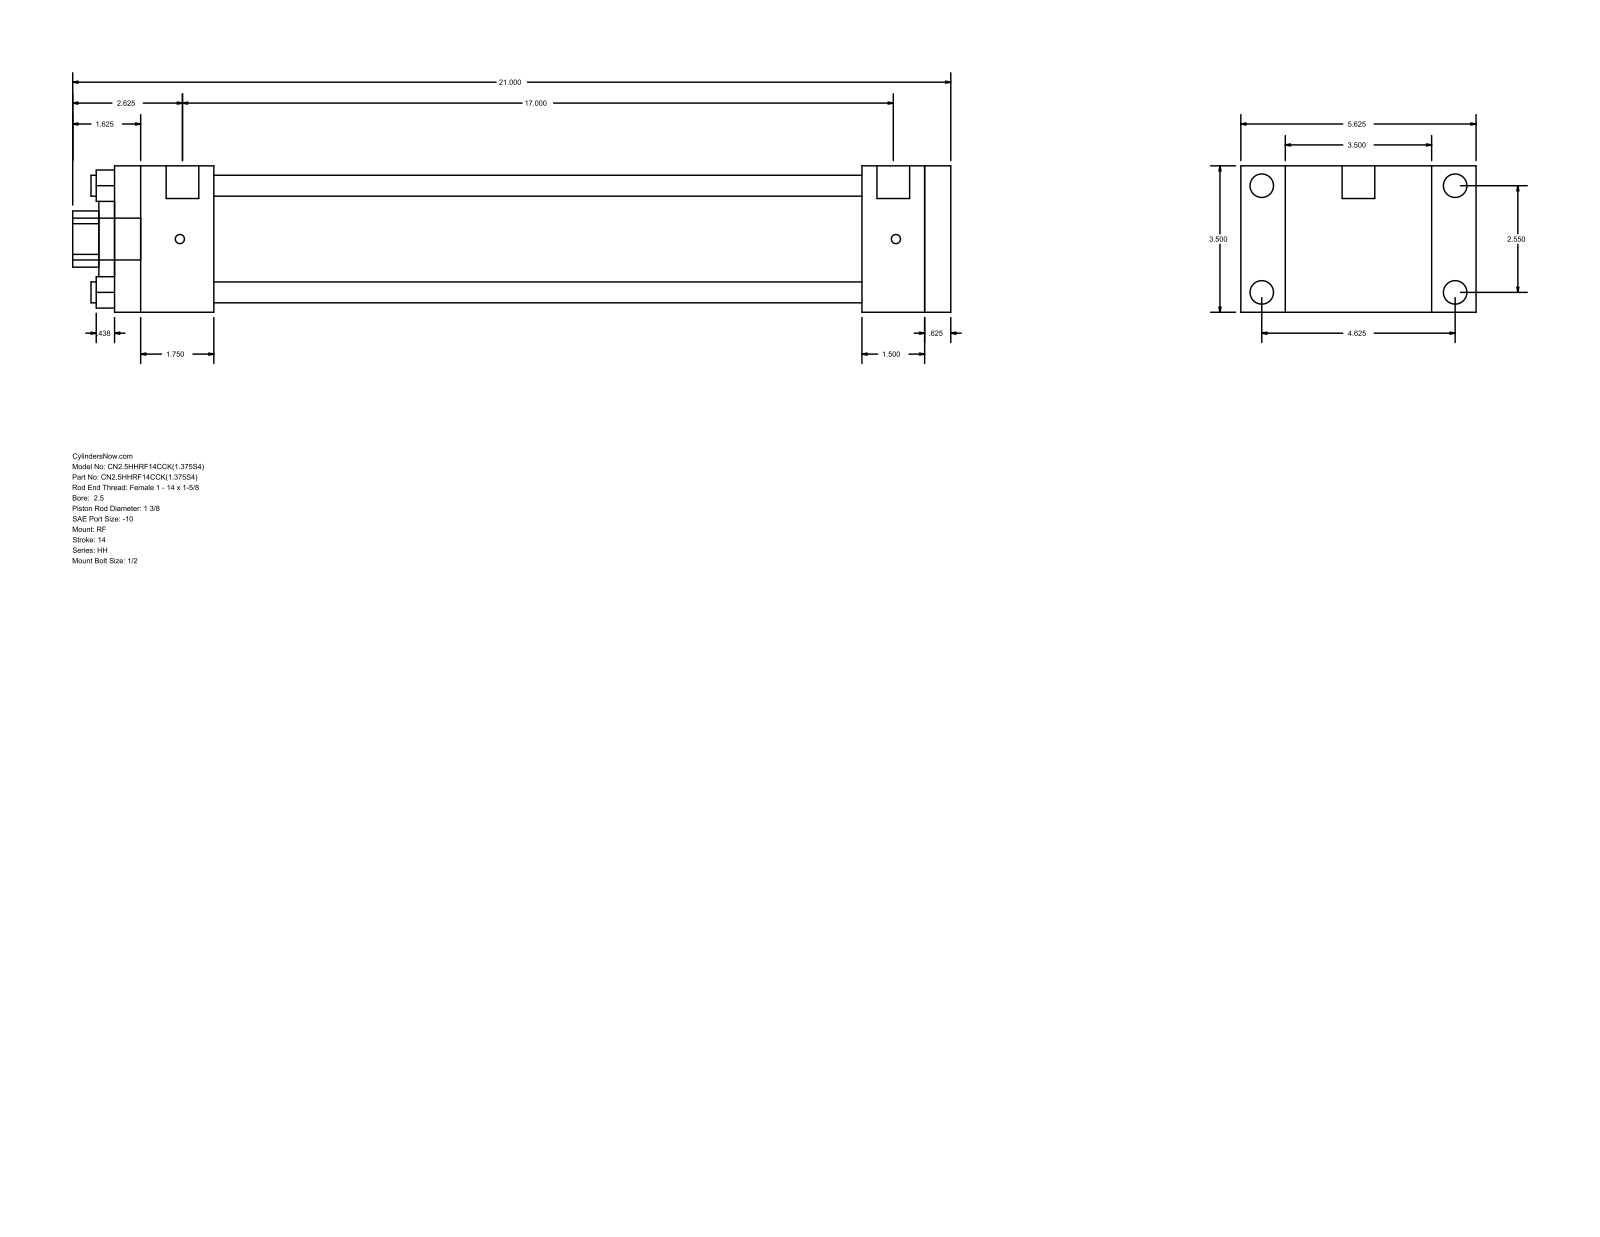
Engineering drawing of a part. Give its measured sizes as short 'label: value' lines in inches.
name: HH_RF__0250_1.375
written by: GSSL Pune (CONFIG_CONTROL_DESIGN)
unit: in
bodies: 0 solids, 92 faces (64 planar, 28 cylindrical, 0 other)
size: 21 × 5.625 × 3.5
holes: 4× ⌀0.5, 1× ⌀1.375, 1× ⌀2, 1× ⌀2.875
bosses: 4× ⌀0.563, 4× ⌀0.219, 2× ⌀0.781, 1× ⌀1
rounds: 1× R0.672
face distances: 3.5, 20, 0.625, 19.375, 2.375, 17, 17.625, 17.875, 15.5, 1.5
hole spacings: 1.803, 2.55, 3.606
